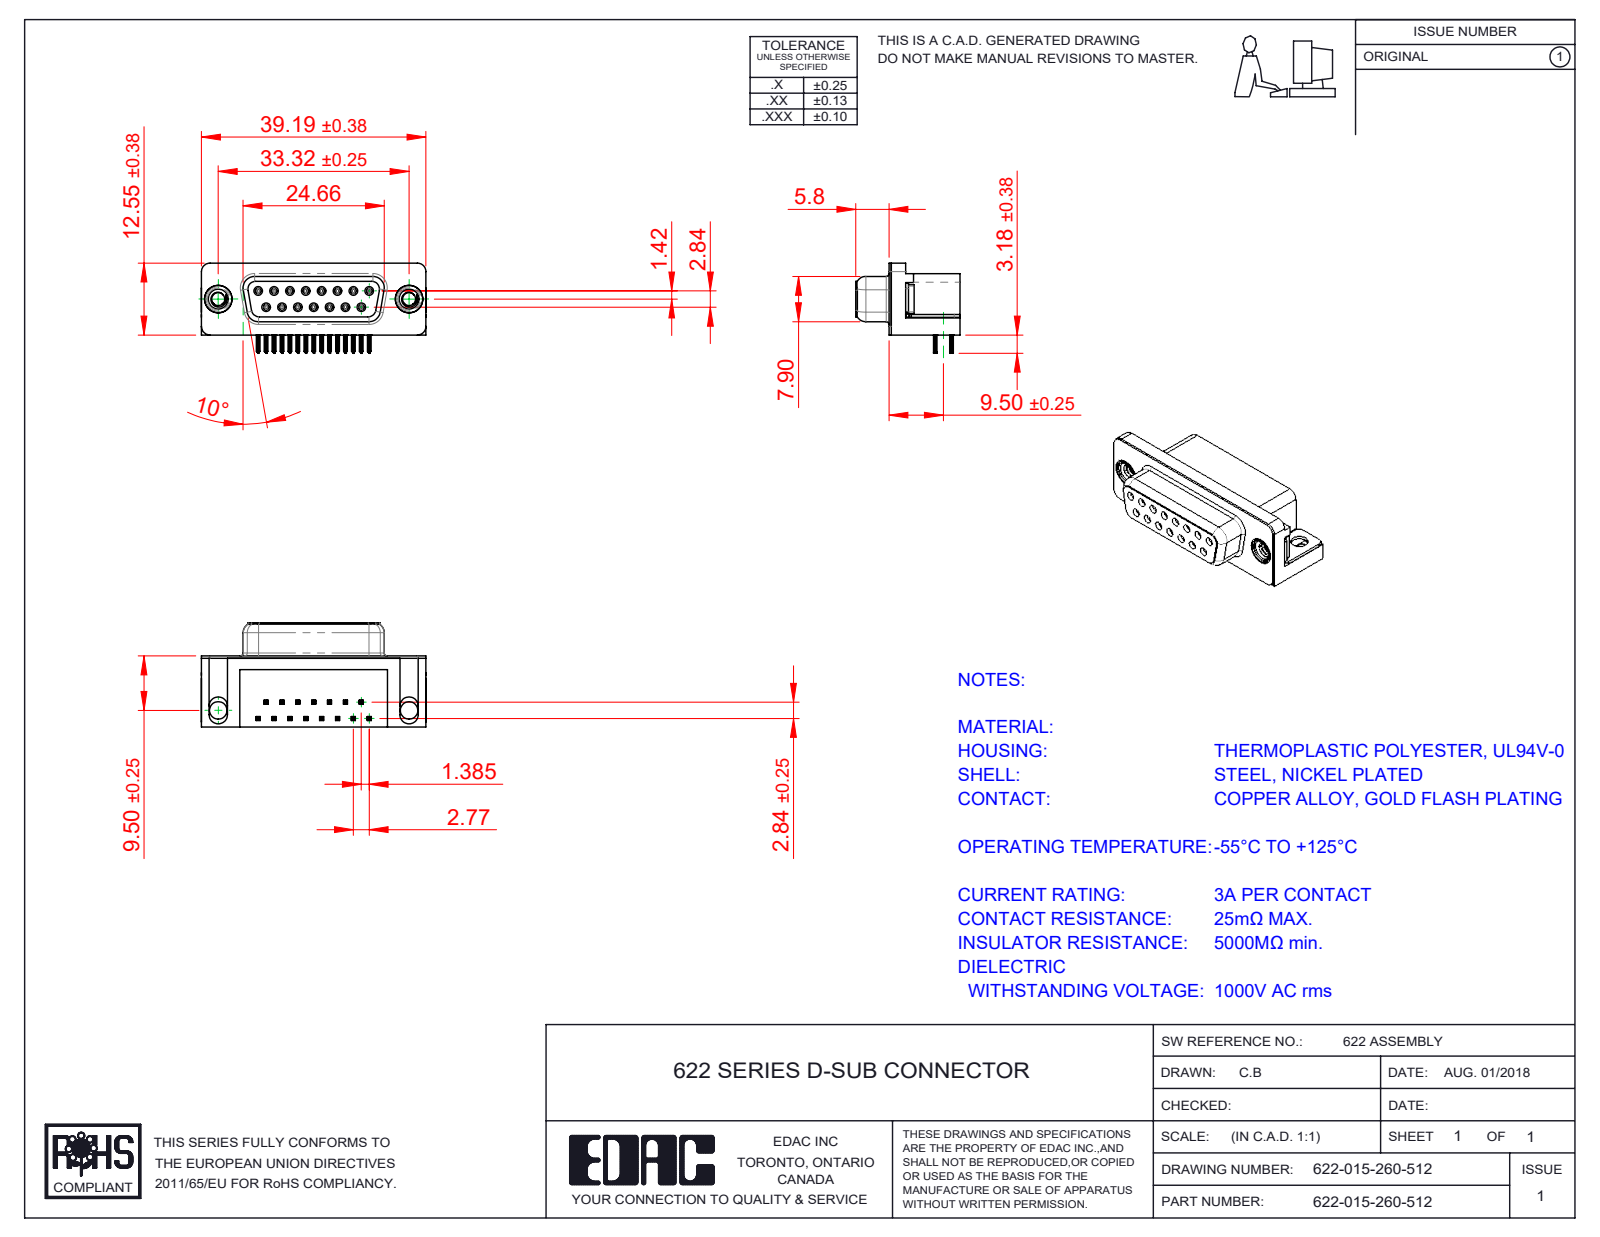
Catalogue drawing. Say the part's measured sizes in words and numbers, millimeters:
The part is named "622 Socket Bottom; 622 Contact Top; 622 Shell_15 Socket; 622-015-260-512 (+3 more)". Its 3-D file was written by "SolidWorks 2016 (CONFIG_CONTROL_DESIGN)". It is 21 solids with 2425 faces: 1072 planar, 605 cylindrical and 748 other. Overall it measures 39.22 by 18.2 by 15.73 millimeters. Its volume is 5 187 cubic millimeters and its surface area 6 703 square millimeters. Round holes: 15 of diameter 0.8, 15 of diameter 0.9, 2 of diameter 2.26, 2 of diameter 3.05, 2 of diameter 4, 2 of diameter 4.8, 2 of diameter 5. Round bosses or shafts: 15 of diameter 1.2, 2 of diameter 4.9, 2 of diameter 4.75, 2 of diameter 3.9. Partial cylindrical surfaces (rounded edges, fillets, slot ends): 120 of radius 0.1, 60 of radius 0.15, 30 of radius 0.35, 18 of radius 1, 15 of radius 0.34, 8 of radius 0.25, 8 of radius 1.35, 8 of radius 1.5. The main face-to-face distances are 0.4, 12, 6.2, 12.4, 10.35, 2.9, 6.65, 0.85, 0.35, 5.8. The hole center spacings are 3.16, 2.77, 5.54, 8.31, 11.08, 5.03, 5.04, 7.48.
